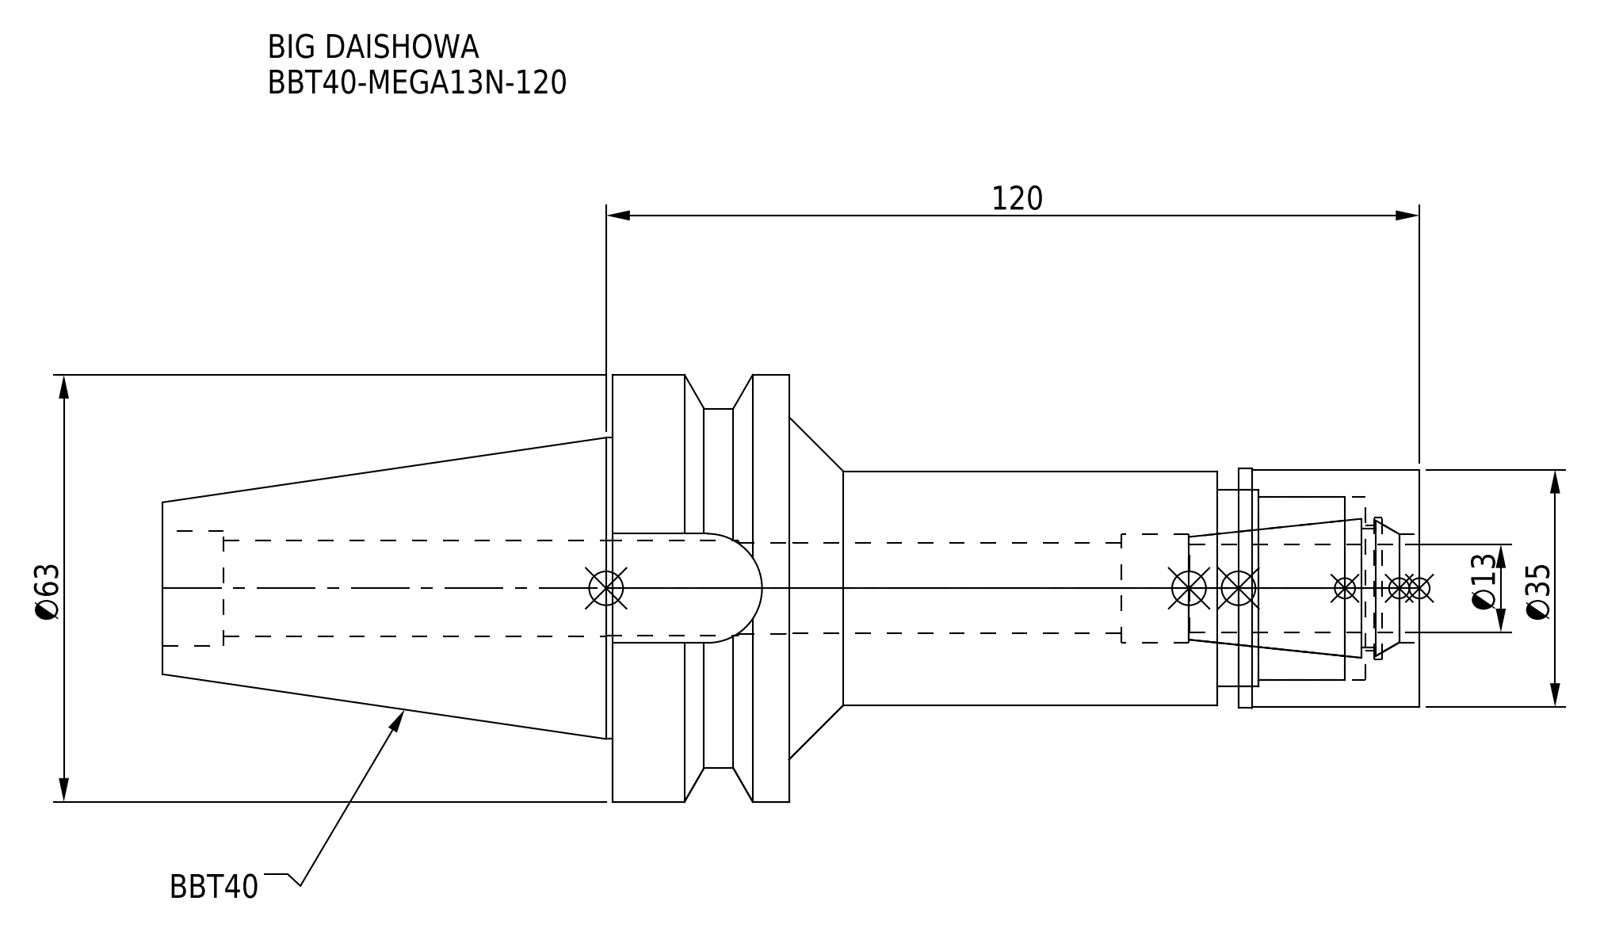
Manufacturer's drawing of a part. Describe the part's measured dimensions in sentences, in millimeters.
The part is named "BBT40-MEGA13N-120_1.stp; DXF_TEMP_ASSY_ASM_4_ASM.stp; MGN13_1.stp; BBT40-MEGA13N-120-130-FreeParts (+3 more)". Its 3-D file was written by "SolidWorks 2019 (CONFIG_CONTROL_DESIGN)". It is 2 solids with 80 faces: 24 planar, 42 cylindrical and 14 other. Overall it measures 185.4 by 63 by 63 millimeters. Its volume is 193 262 cubic millimeters and its surface area 41 126 square millimeters. Round holes: 1 of diameter 13.3, 1 of diameter 13.5, 1 of diameter 14, 1 of diameter 14.2, 1 of diameter 16, 1 of diameter 17, 1 of diameter 18.5, 1 of diameter 21, 1 of diameter 27, 1 of diameter 29. Round bosses or shafts: 1 of diameter 63, 1 of diameter 53, 1 of diameter 44.45, 1 of diameter 35.3, 1 of diameter 35, 1 of diameter 34.5. Partial cylindrical surfaces (rounded edges, fillets, slot ends): 1 of radius 8.05. The main face-to-face distances are 26, 93, 119, 85, 45, 26.7, 66.3, 92.3, 8, 18.7.
